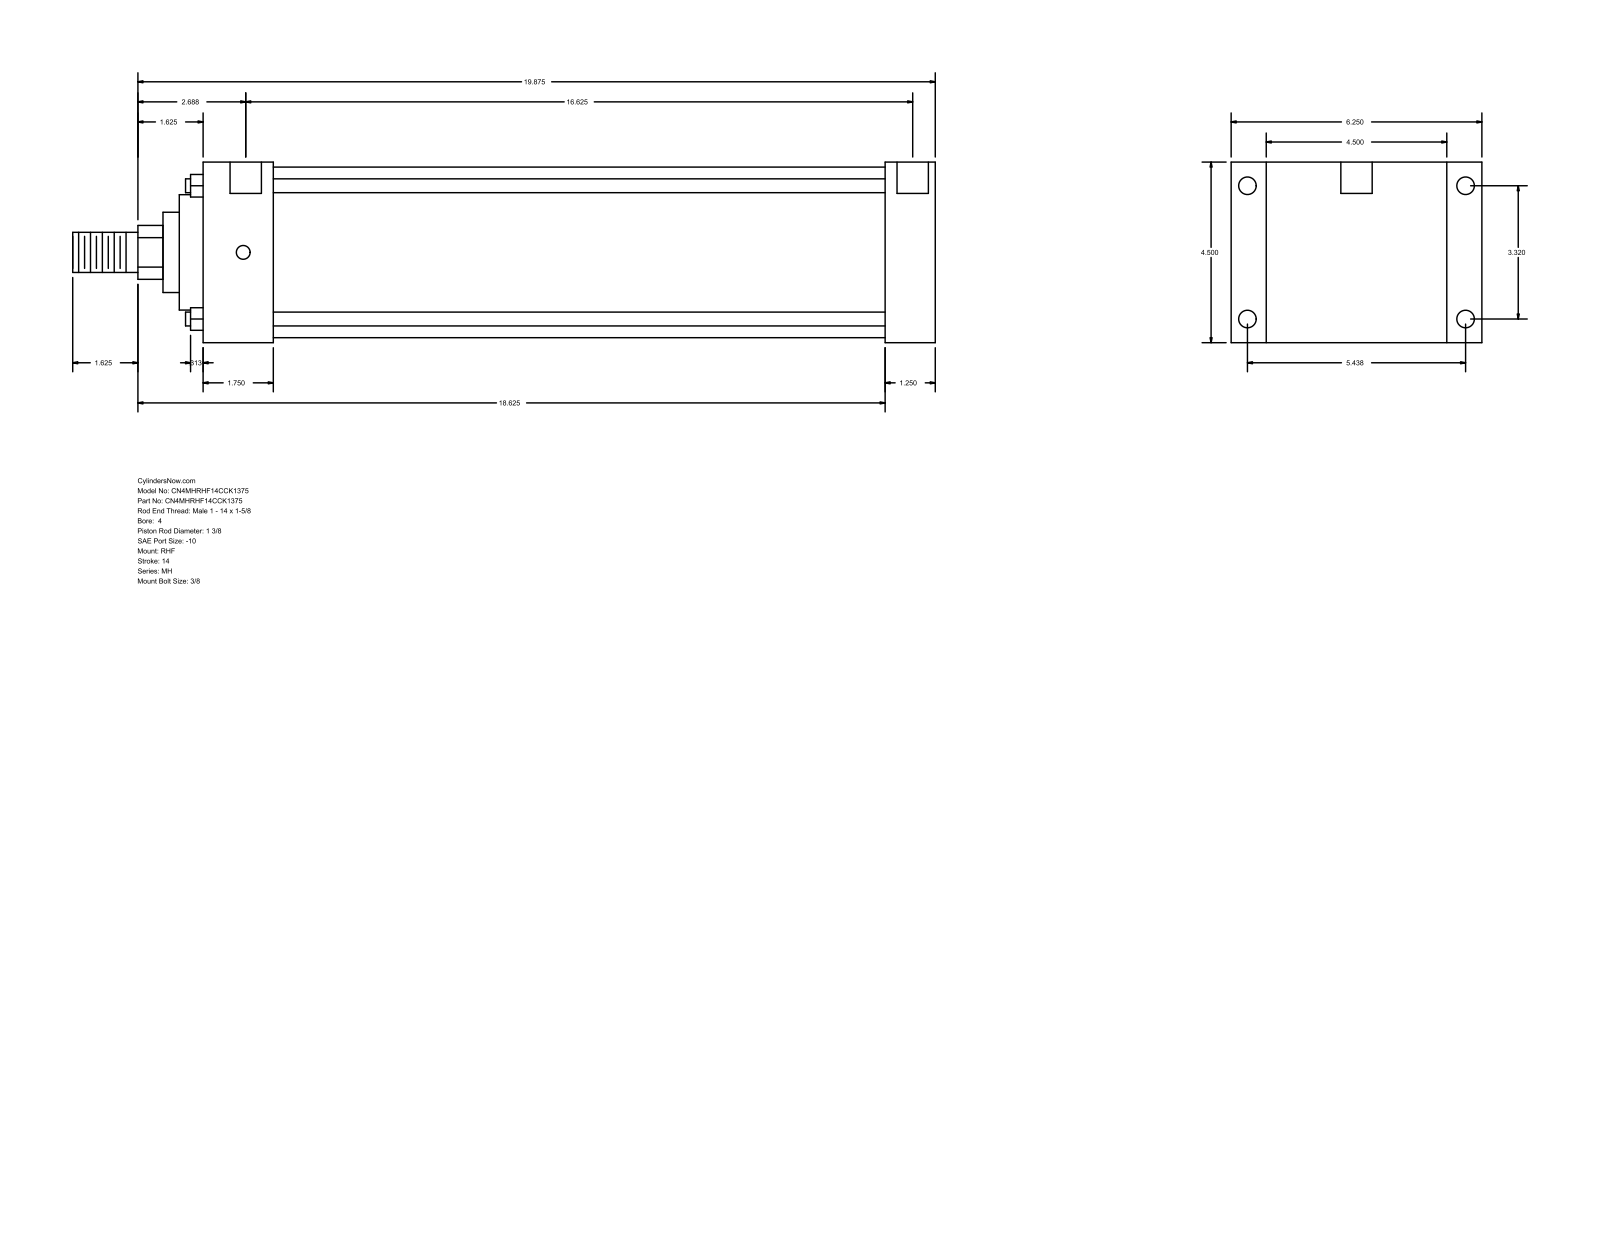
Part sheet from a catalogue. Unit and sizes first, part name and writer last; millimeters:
Units: millimetres
Overall size (bounding box): 546.1 × 158.75 × 114.3
Round holes (diameter × count): ⌀8.73 ×4, ⌀11.13 ×4, ⌀19.84 ×2
Round bosses / shafts (diameter × count): ⌀8.76 ×4, ⌀107.95 ×1, ⌀73.03 ×1, ⌀50.8 ×1, ⌀34.92 ×1, ⌀25.4 ×1
Partial cylindrical surfaces — rounded edges, fillets, slot ends (radius × count): R17.06 ×1
Main face-to-face distances: 114.3, 31.75, 431.8, 463.55, 22.23, 136.53, 44.45, 387.35, 419.1, 158.76
Hole centre spacings: 84.32, 138.12, 161.82, 425.45, 1.58, 1.59, 422.28, 423.86
Bodies: 0 solids, 90 faces (61 planar, 29 cylindrical, 0 other)
Part name (STEP PRODUCT): MH_RHF__0400_1.375
STEP written by: GSSL Pune (CONFIG_CONTROL_DESIGN)
